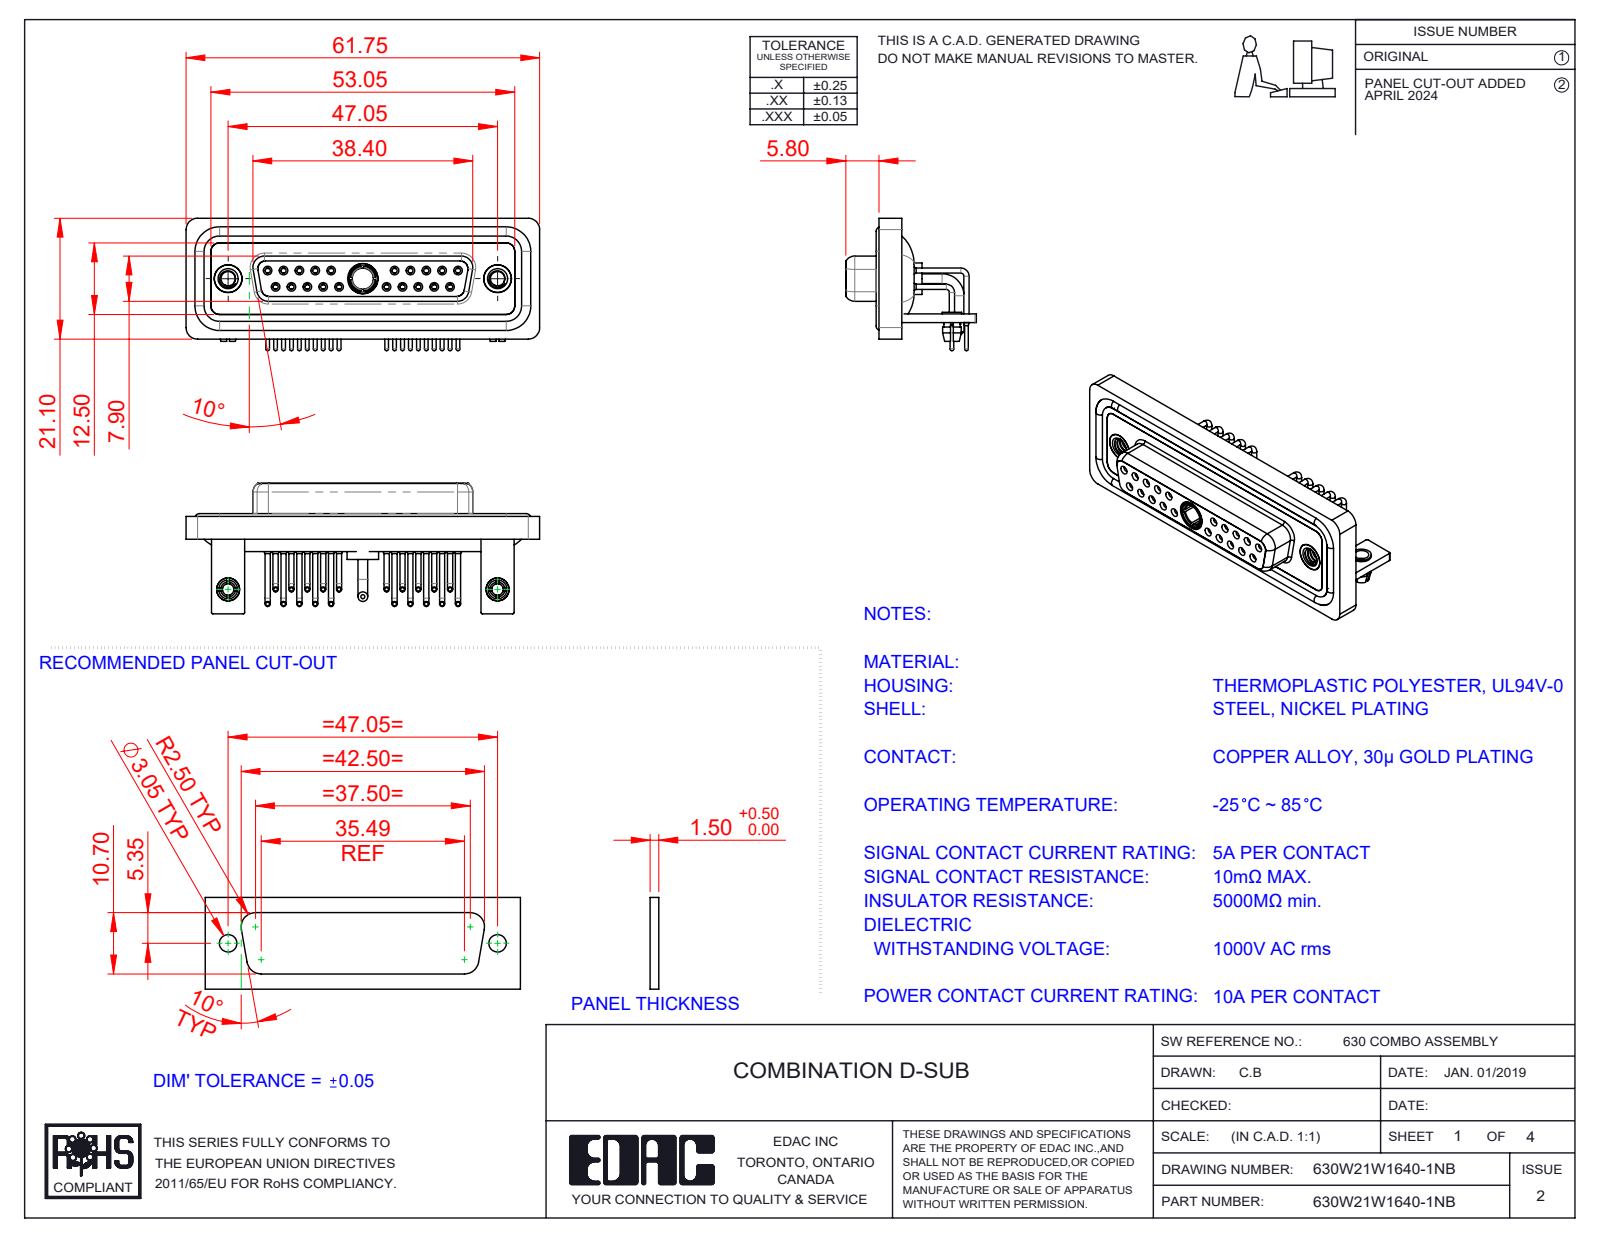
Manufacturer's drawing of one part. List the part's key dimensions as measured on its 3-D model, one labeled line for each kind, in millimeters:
Part name (STEP PRODUCT): 630Combo Stabilizer Bracket_50 Contacts; Power Socket_10A RA; 630Combo Contact Row 2_50 Contacts; 630Combo Contact Row 1_50 Contacts (+7 more)
STEP written by: SolidWorks 2023 (CONFIG_CONTROL_DESIGN)
Units: millimetres
Bodies: 33 solids, 1658 faces (502 planar, 727 cylindrical, 429 other)
Overall size (bounding box): 61.75 × 23.12 × 22.8
Volume: 8 843 mm³ · Surface area: 15 678 mm²
Round holes (diameter × count): ⌀2 ×22, ⌀0.9 ×20, ⌀1.1 ×20, ⌀1.5 ×20, ⌀1.6 ×10, ⌀1.7 ×10, ⌀2.5 ×4, ⌀4.85 ×3, ⌀3.2 ×2, ⌀4 ×2, ⌀4.05 ×2, ⌀5 ×2
Round bosses / shafts (diameter × count): ⌀0.9 ×20, ⌀0.65 ×20, ⌀1.6 ×14, ⌀4.95 ×2, ⌀4.8 ×2, ⌀4 ×2, ⌀3.4 ×2, ⌀3.3 ×2
Partial cylindrical surfaces — rounded edges, fillets, slot ends (radius × count): R2 ×19, R1.5 ×18, R0.25 ×16, R1.35 ×8, R1.6 ×8, R0.5 ×5, R0.6 ×4, R0.65 ×4
Main face-to-face distances: 0.4, 1.8, 2.9, 3.7, 1.5, 4.1, 1.1, 1.4, 1.6, 2.5
Hole centre spacings: 3.16, 2.77, 5.54, 8.31, 5.04, 19.39, 20.97, 22.16
